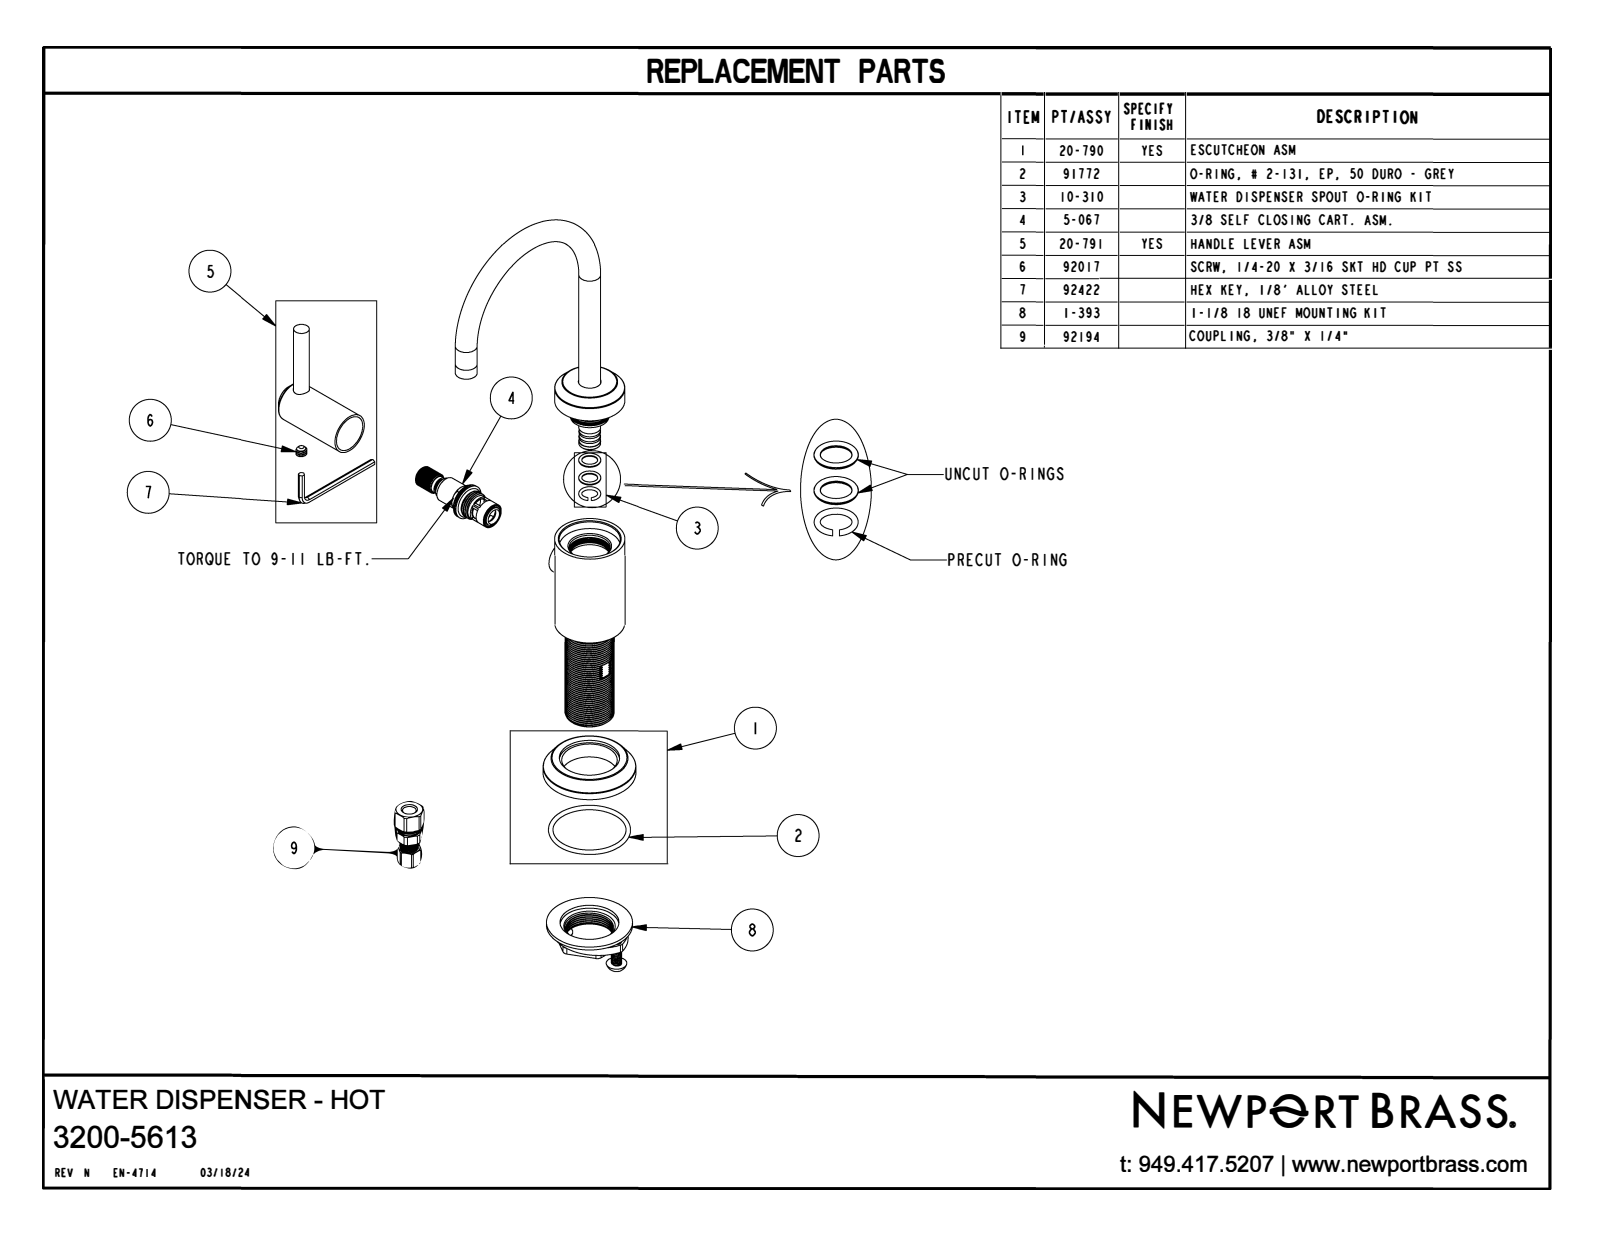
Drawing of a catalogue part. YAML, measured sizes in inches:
part_name: "3200-5613"
step_written_by: "CREO PARAMETRIC BY PTC INC, 2018400 (CONFIG_CONTROL_DESIGN)"
units: inches
bodies: {solids: 1, faces: 44, planar: 8, cylindrical: 16, other: 20}
overall_size: [9.275, 5.313, 3.648]
volume: 10.65
surface_area: 47.86
round_holes:
  - {diameter: 0.375, count: 1}
  - {diameter: 1, count: 1}
round_bosses_or_shafts:
  - {diameter: 0.5, count: 2}
  - {diameter: 2.125, count: 1}
  - {diameter: 1.61, count: 1}
  - {diameter: 0.95, count: 1}
  - {diameter: 0.36, count: 1}
face_to_face_distances: [3.306, 0.425, 2.881, 6.525, 6.1, 3.219, 4.117, 3.692, 0.811, 2.408]
